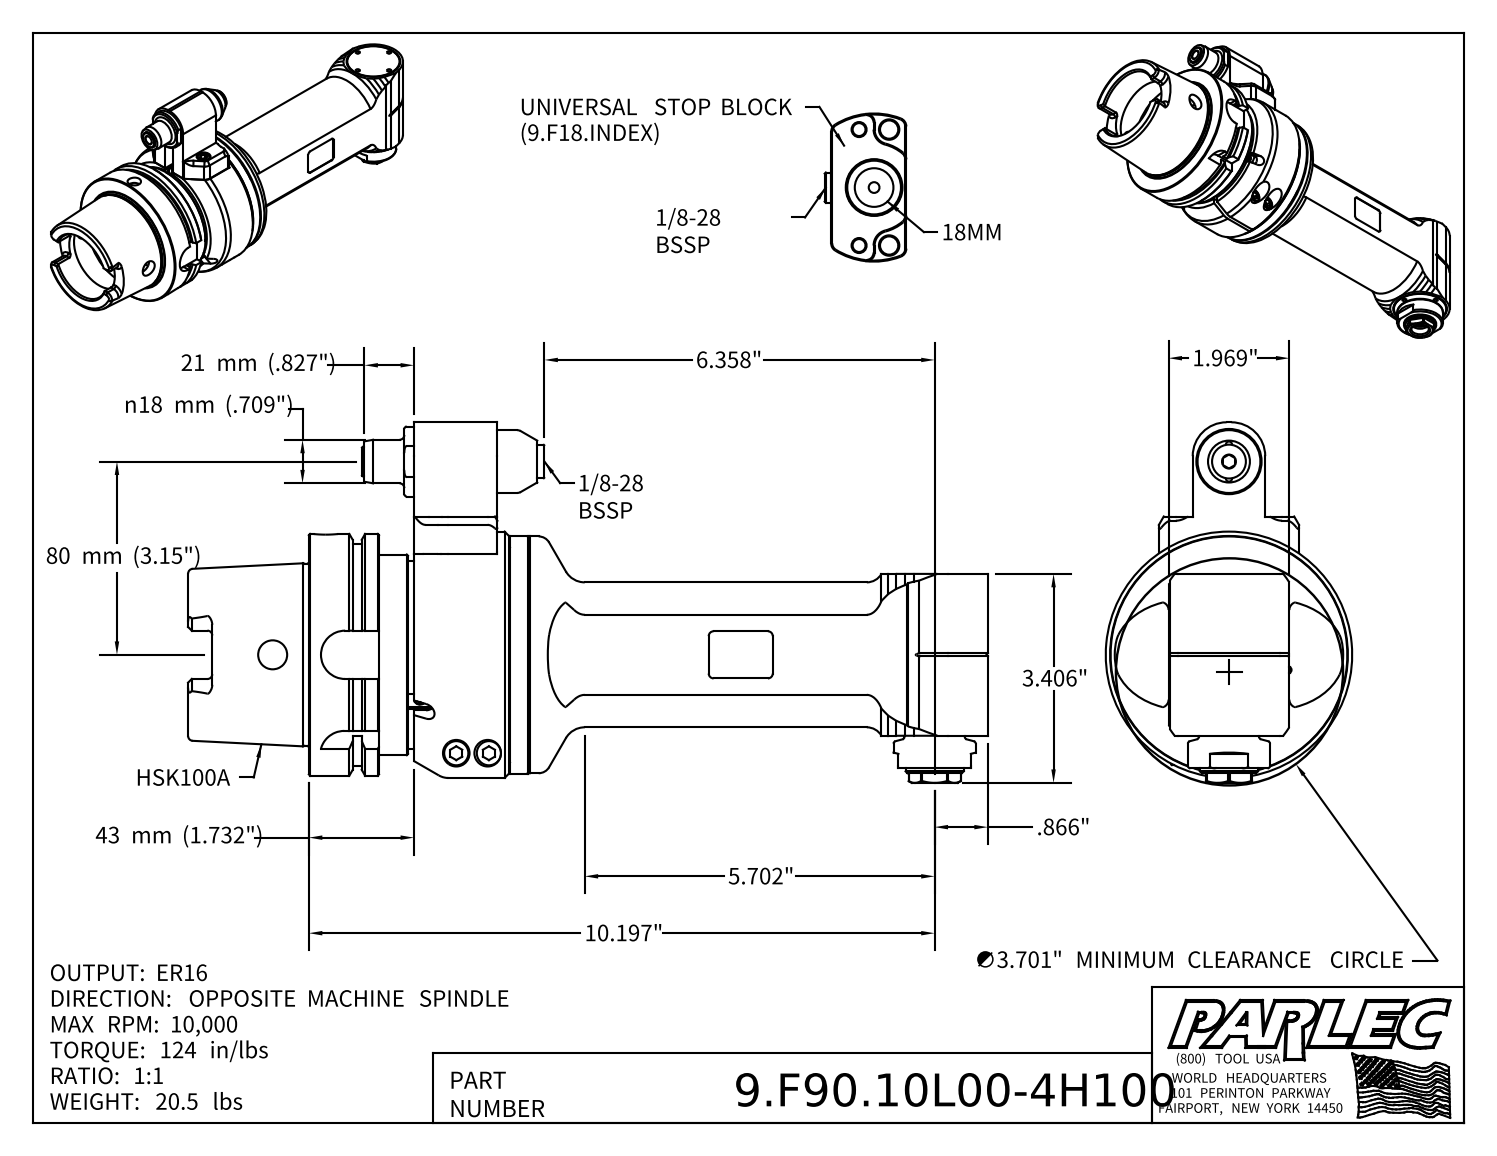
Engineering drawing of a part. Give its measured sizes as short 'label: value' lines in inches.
name: 9.F90.10L00-4H100; 9_F90_10L00; 9_GA1_518_2 (EVO, Type 1, H100A, 80mm)
written by: Autodesk Inventor 2022 (AUTOMOTIVE_DESIGN)
unit: in
bodies: 7 solids, 606 faces (272 planar, 162 cylindrical, 172 other)
size: 13.031 × 5.876 × 4.016
volume: 80.06 in³; area: 297.1 in²
holes: 20× ⌀0.335, 4× ⌀0.126, 4× ⌀0.197, 3× ⌀0.433, 2× ⌀0.102, 2× ⌀0.409, 2× ⌀0.472, 2× ⌀0.965, 1× ⌀0.098, 1× ⌀0.118, 1× ⌀0.256, 1× ⌀0.276
bosses: 4× ⌀0.394, 4× ⌀0.236, 2× ⌀0.709, 2× ⌀0.315, 2× ⌀0.098, 1× ⌀4.016, 1× ⌀3.937, 1× ⌀3.874
rounds: 18× R0.079, 5× R0.157, 4× R0.192, 4× R0.394, 2× R0.016, 2× R0.02, 2× R0.039, 2× R0.138
face distances: 1.26, 1.555, 1.969, 1.142, 1.22, 0.65, 2.008, 1.575, 3.268, 1.024
hole spacings: 1.516, 2.144, 1.824, 3.002, 0.835, 2.651, 2.914, 3.031
